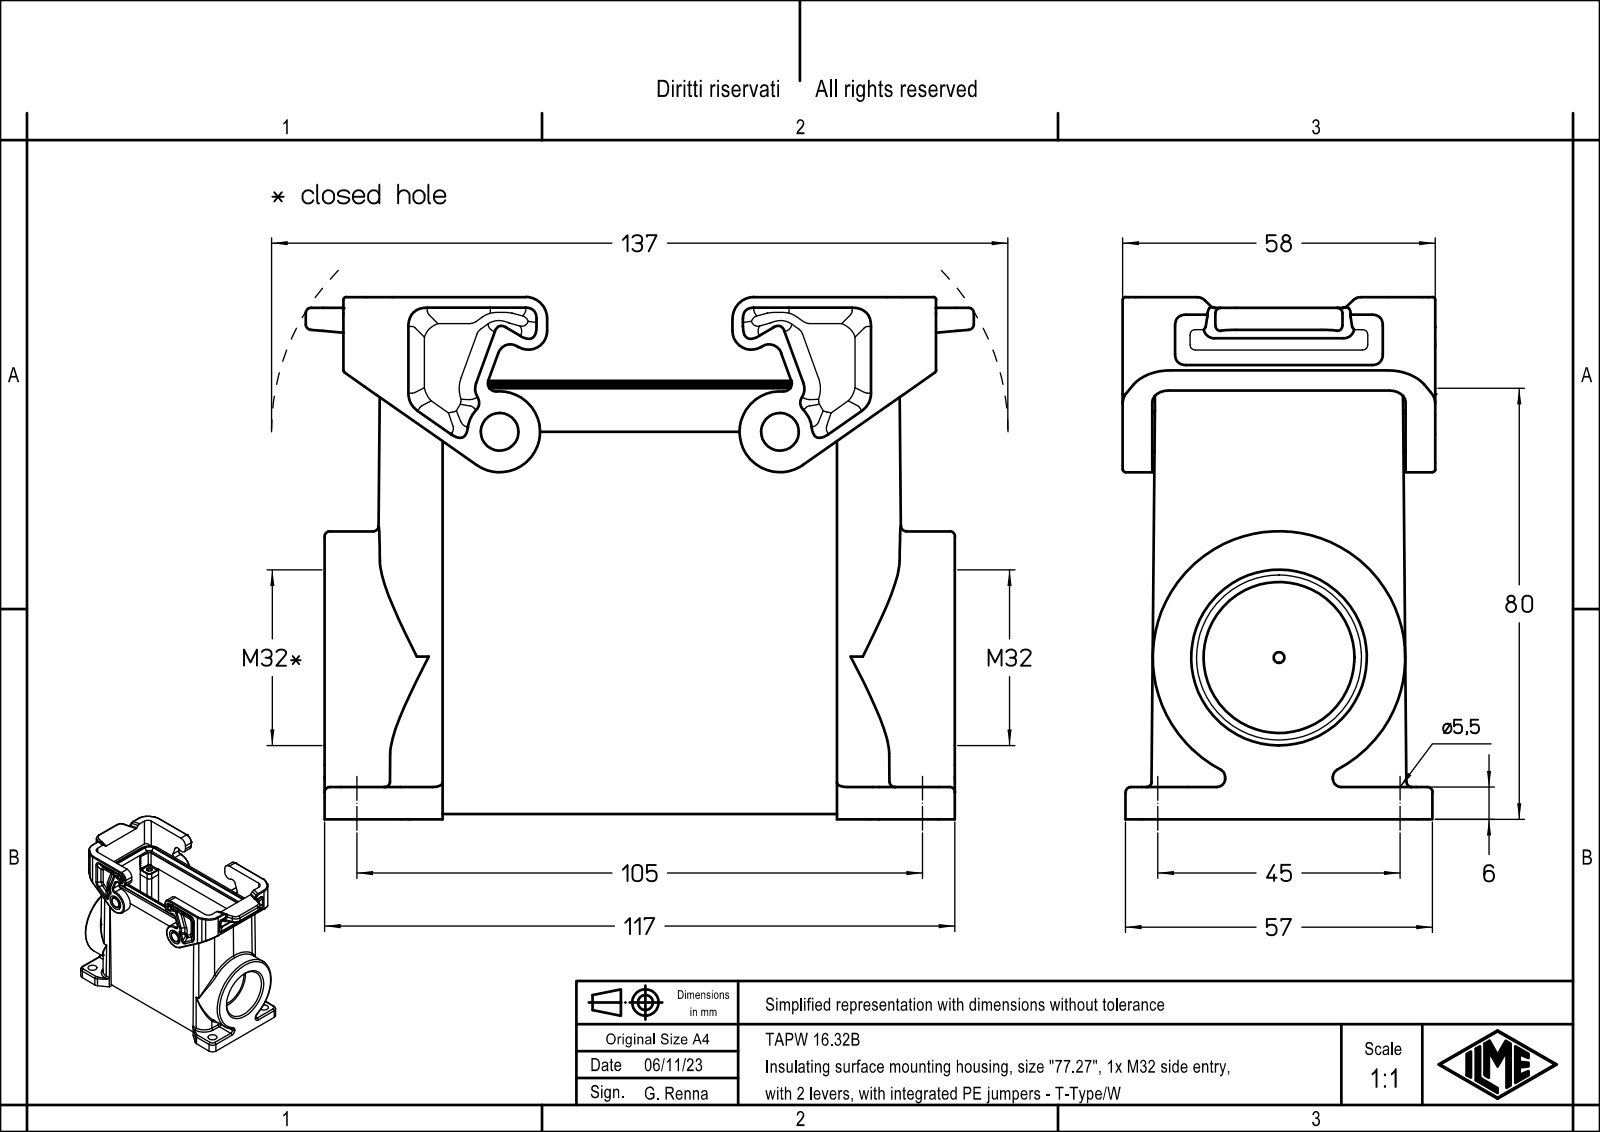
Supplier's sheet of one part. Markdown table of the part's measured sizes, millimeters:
| quantity | value |
| --- | --- |
| part name | TAPW 16.32B |
| STEP written by | Creo Elements/Direct Modeling 20.1B 02-Apr-2019 (C) Parametric Technology GmbH (AUTOMOTIVE_DESIGN) |
| units | millimeters |
| bodies | 1 solid, 610 faces (364 planar, 194 cylindrical, 52 other) |
| overall size | 124 × 96.9 × 58 |
| volume | 198 944 mm³ |
| surface area | 73 592 mm² |
| round holes (diameter × count) | 3.5 × 4, 5.5 × 4, 28 × 1, 30.6 × 1 |
| round bosses / shafts (diameter × count) | 7 × 2, 46.87 × 1 |
| partial cylindrical surfaces (radius × count) | 2 × 20, 3 × 20, 1.5 × 18, 1 × 16, 1.3 × 12, 6 × 8, 7 × 8, 4 × 6 |
| main face-to-face distances | 35.2, 5.5, 5.9, 41.1, 6.5, 1, 11.4, 46.6, 52.5, 11.8 |
| hole center spacings | 16.43, 38.54, 91.69, 98.09, 27, 45, 77.5, 82.07 |
